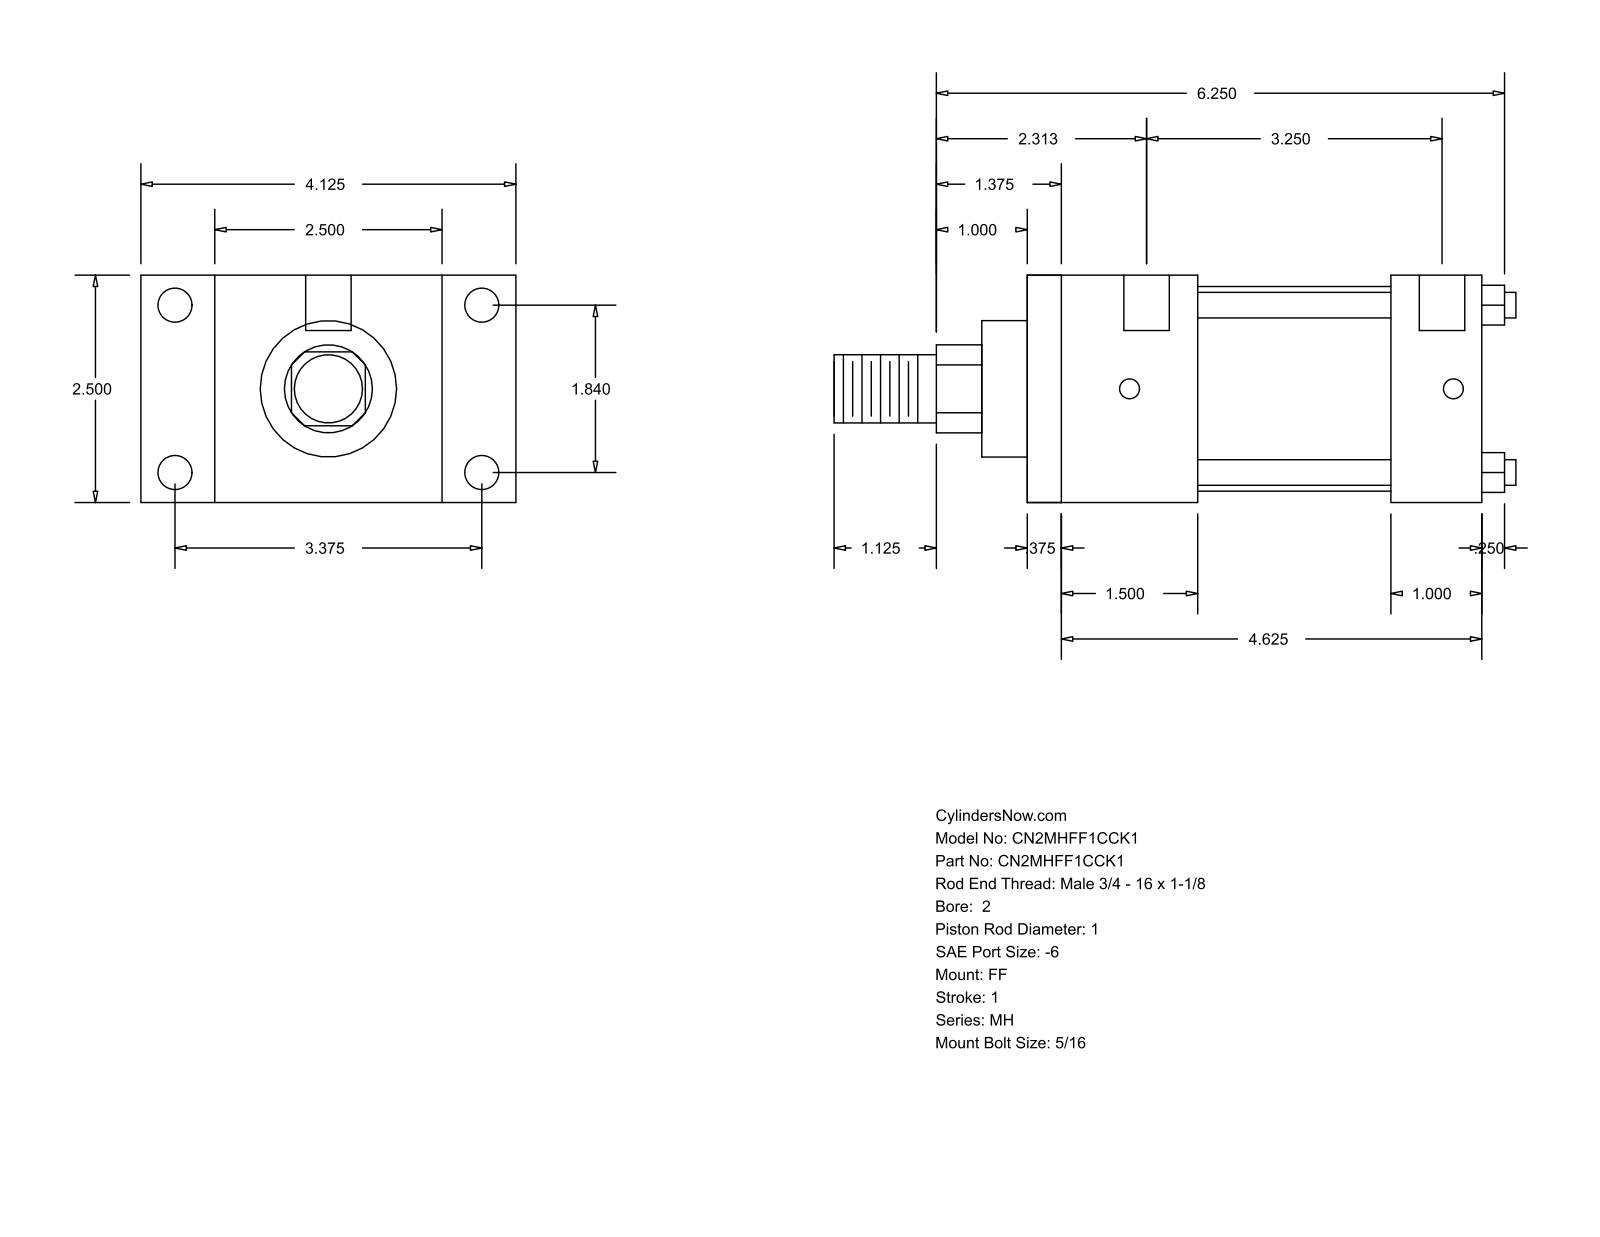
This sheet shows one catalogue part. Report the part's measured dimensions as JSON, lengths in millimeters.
{"part_name": "MH_FF__0200_1", "step_written_by": "GSSL Pune (CONFIG_CONTROL_DESIGN)", "units": "millimeters", "bodies": {"solids": 0, "faces": 92, "planar": 64, "cylindrical": 28, "other": 0}, "overall_size": [190.5, 104.78, 63.5], "round_holes": [[5.56, 4], [9.53, 4], [12.7, 2]], "round_bosses_or_shafts": [[7.14, 4], [57.15, 1], [38.1, 1], [25.4, 1], [19.05, 1]], "partial_cylinders_radius": [[12.29, 1]], "face_to_face_distances": [63.5, 127, 9.52, 117.48, 53.97, 101.6, 20.64, 25.4, 47.63, 38.11], "hole_center_spacings": [85.72, 46.74, 90.48, 97.63, 3.17, 4.76, 82.55, 87.31]}
